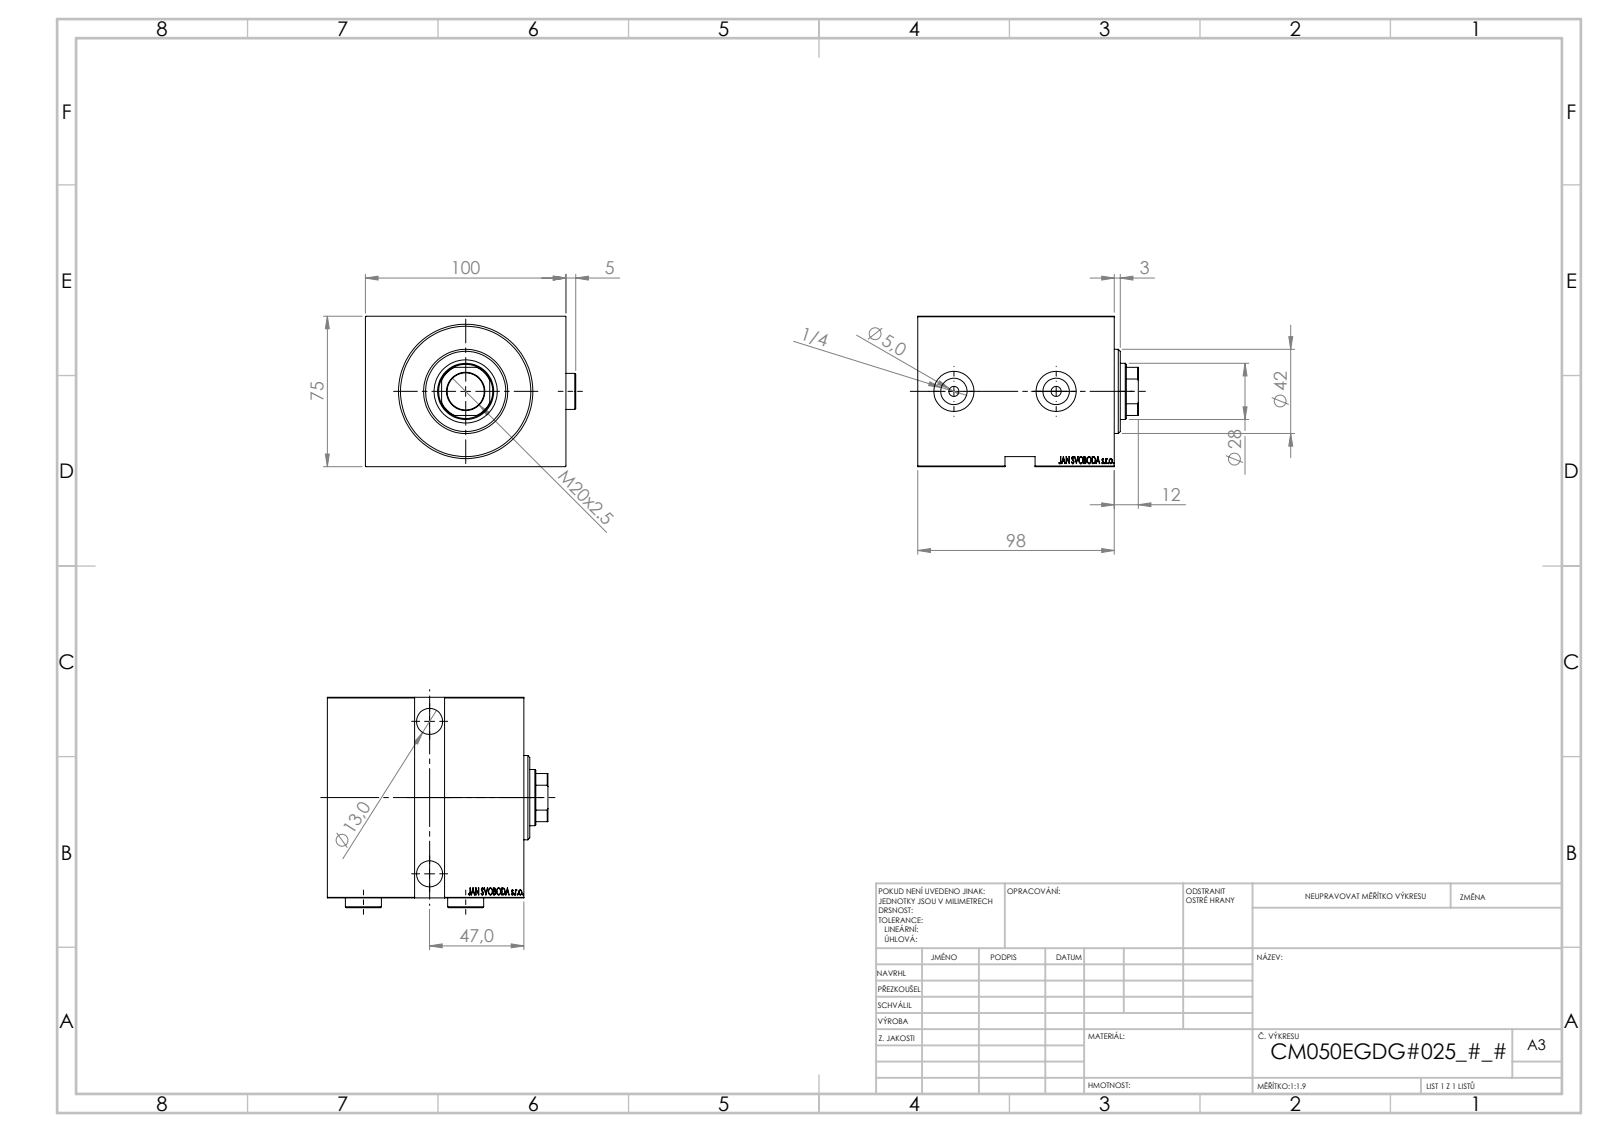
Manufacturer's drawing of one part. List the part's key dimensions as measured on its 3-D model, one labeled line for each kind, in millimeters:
Part name (STEP PRODUCT): V450CM_E_VCP; V450CM_E_Body; V450CM_VC_B; Zatka_OIL_PORT
STEP written by: SolidWorks 2019 (CONFIG_CONTROL_DESIGN)
Units: millimetres
Bodies: 5 solids, 902 faces (444 planar, 60 cylindrical, 398 other)
Overall size (bounding box): 110 × 104.9 × 75
Volume: 672 458 mm³ · Surface area: 101 365 mm²
Round holes (diameter × count): ⌀5 ×2, ⌀13 ×2, ⌀13.16 ×2, ⌀19 ×2, ⌀20 ×2, ⌀18.5 ×1, ⌀28 ×1, ⌀31.5 ×1, ⌀50 ×1, ⌀65 ×1
Round bosses / shafts (diameter × count): ⌀18 ×2, ⌀52 ×1, ⌀42 ×1
Partial cylindrical surfaces — rounded edges, fillets, slot ends (radius × count): R13.5 ×1
Main face-to-face distances: 75, 100, 98, 5, 14, 84, 79, 93, 81.4, 67.4
Hole centre spacings: 51, 76
